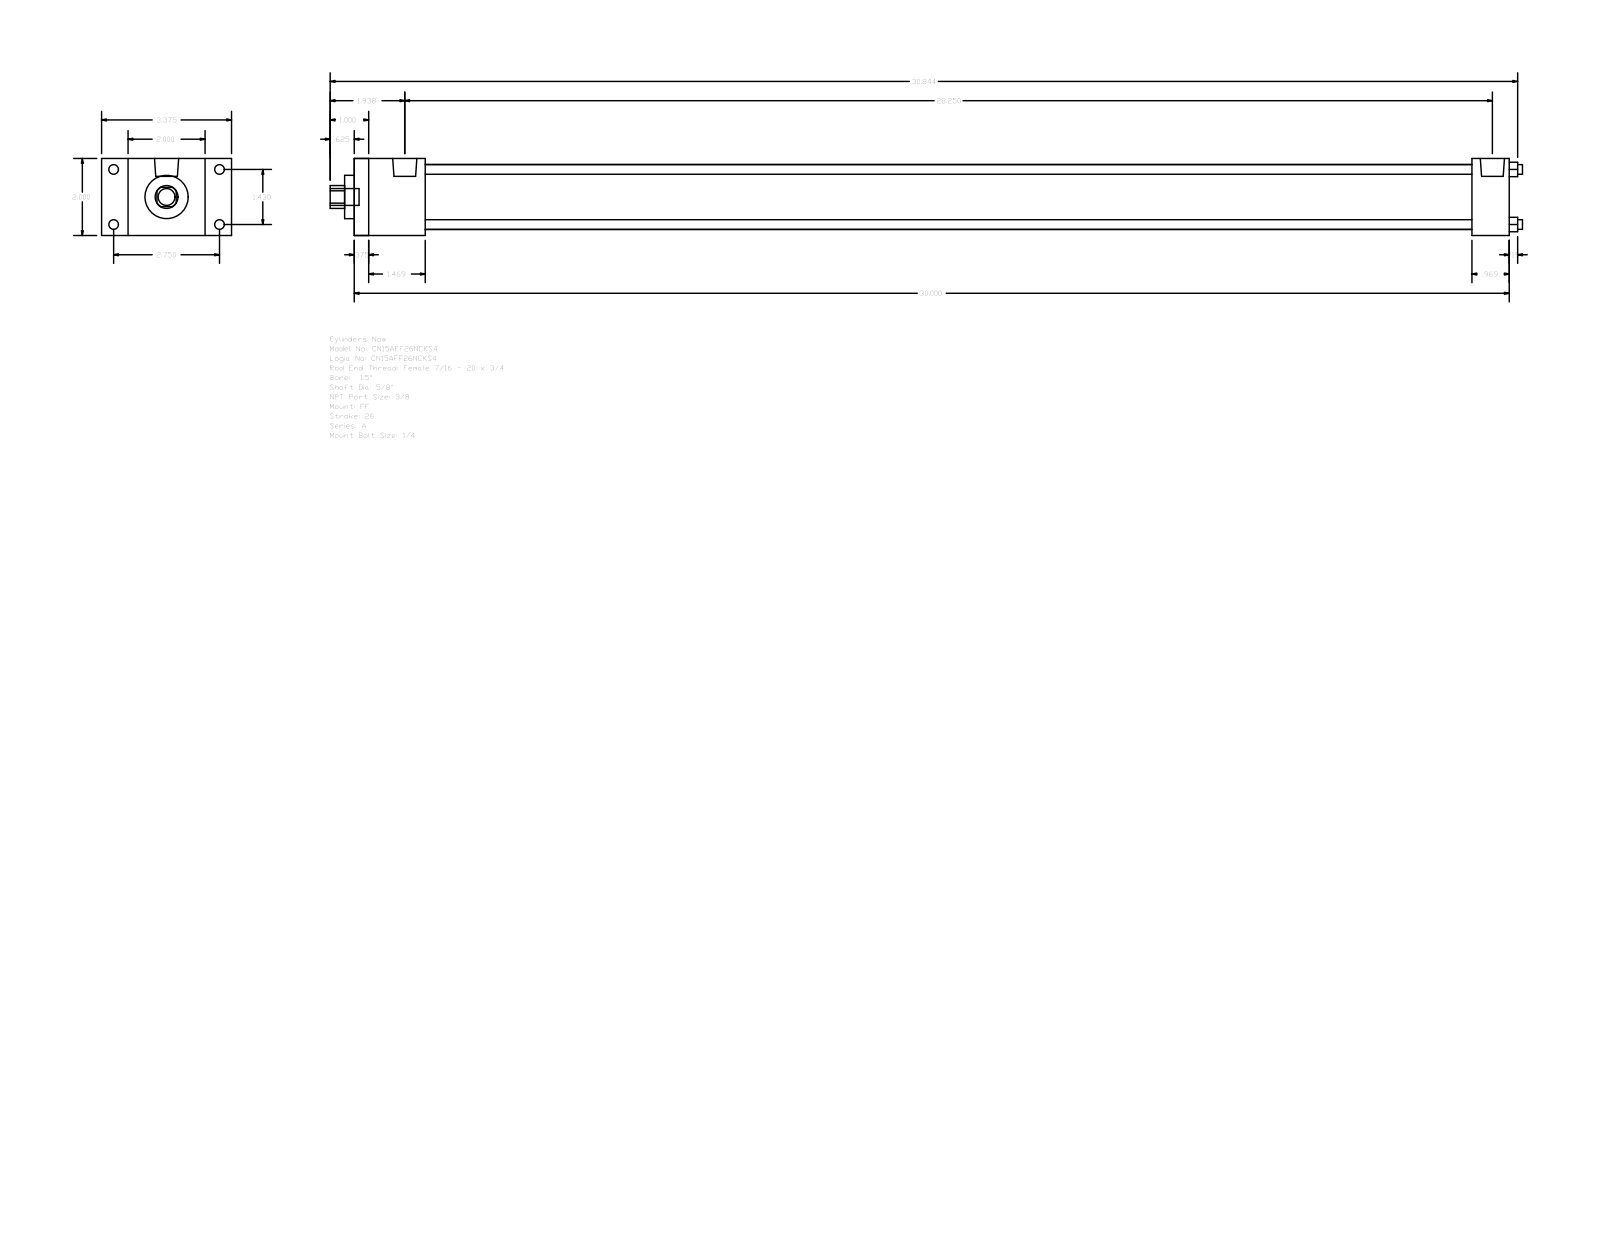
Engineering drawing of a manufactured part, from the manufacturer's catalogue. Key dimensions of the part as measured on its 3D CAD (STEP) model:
Part name (STEP PRODUCT): A_FF__0150_0.625
STEP written by: GSSL Pune (CONFIG_CONTROL_DESIGN)
Units: millimetres
Bodies: 0 solids, 92 faces (64 planar, 28 cylindrical, 0 other)
Overall size (bounding box): 786.61 × 85.72 × 50.8
Round holes (diameter × count): ⌀6.35 ×4, ⌀15.88 ×1, ⌀28.57 ×1, ⌀42.93 ×1
Round bosses / shafts (diameter × count): ⌀6.35 ×4, ⌀5.56 ×4, ⌀15.93 ×2, ⌀11.11 ×1
Partial cylindrical surfaces — rounded edges, fillets, slot ends (radius × count): R7.54 ×1
Main face-to-face distances: 50.8, 762, 9.52, 752.48, 46.83, 737.39, 37.31, 727.87, 690.56, 715.17
Hole centre spacings: 25.68, 36.32, 51.36
